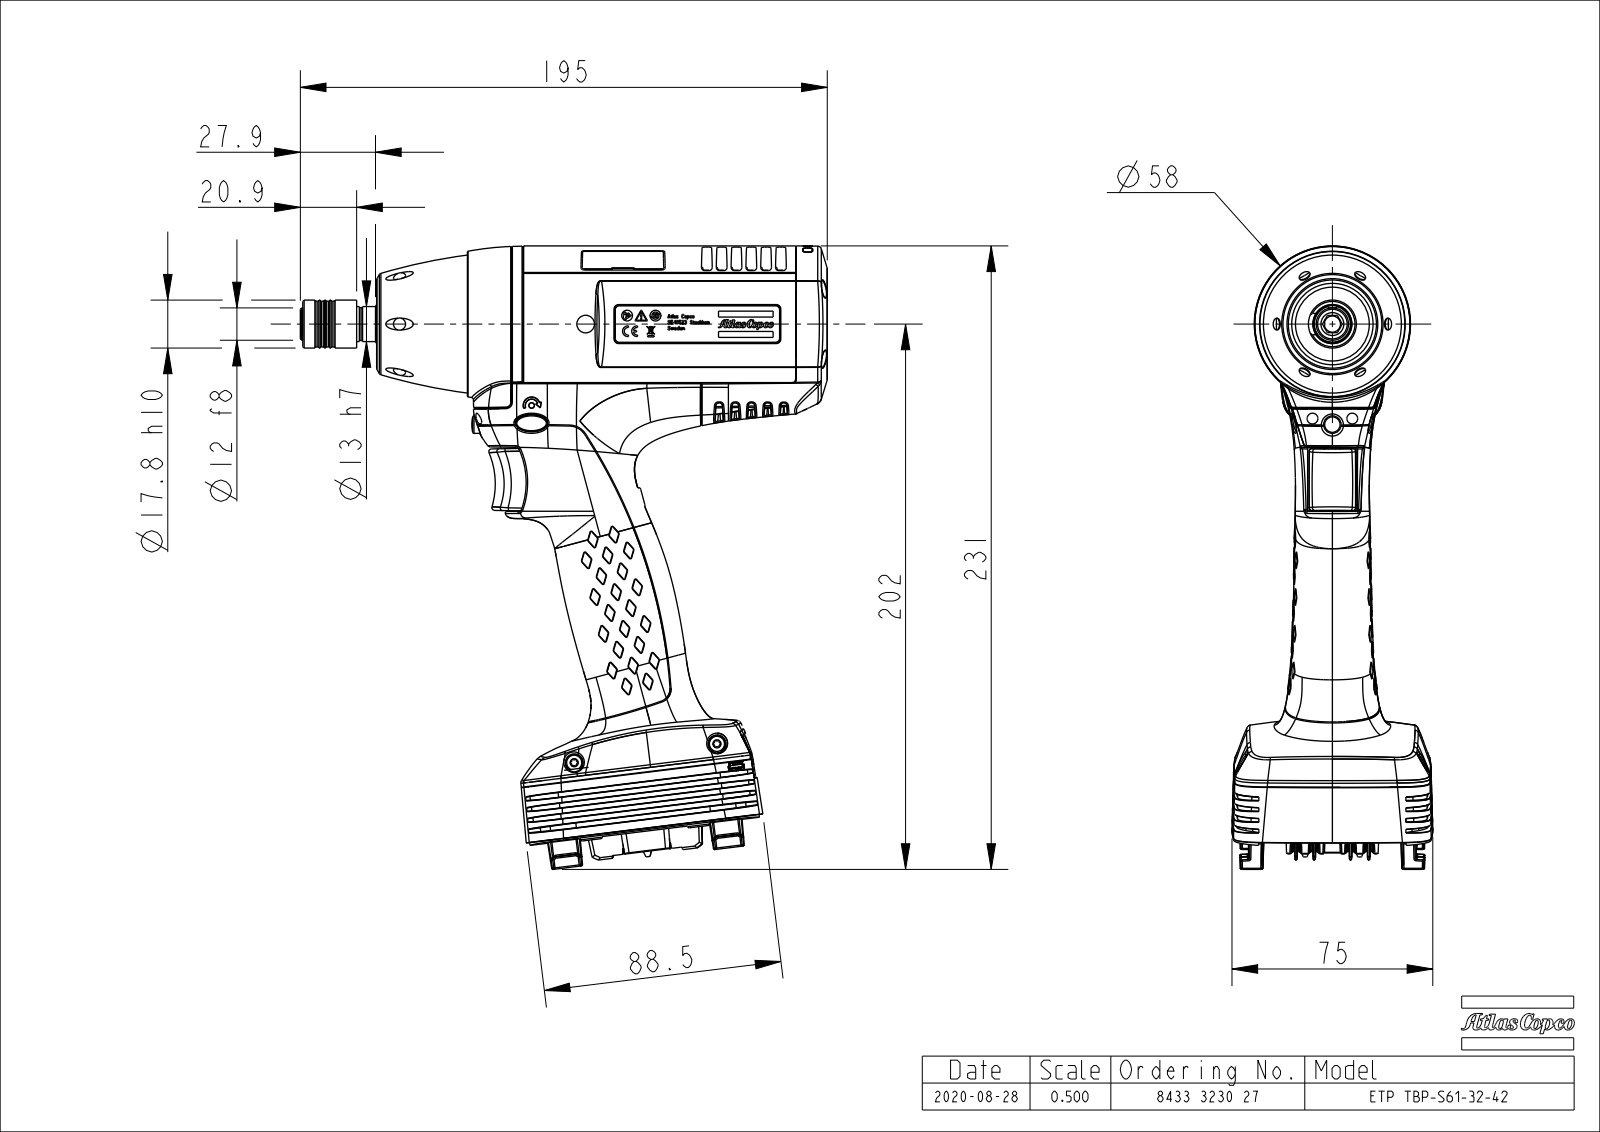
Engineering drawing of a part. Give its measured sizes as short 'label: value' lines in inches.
name: EXT_COMP_SW0001; PRT0009; PRT0015; 4250313204 (+1 more)
written by: CREO PARAMETRIC BY PTC INC, 2020281 (AP242_MANAGED_MODEL_BASED_3D_ENGINEERING_MIM_LF)
unit: in
bodies: 10 solids, 5885 faces (2462 planar, 1217 cylindrical, 2206 other)
size: 9.108 × 7.701 × 2.935
volume: 48.95 in³; area: 178.7 in²
holes: 3× ⌀0.126, 3× ⌀0.157, 3× ⌀0.177, 2× ⌀0.094, 2× ⌀0.138, 1× ⌀0.008, 1× ⌀0.016, 1× ⌀0.023, 1× ⌀0.04, 1× ⌀0.193, 1× ⌀0.22, 1× ⌀0.236
bosses: 7× ⌀0.22, 4× ⌀0.118, 1× ⌀1.457, 1× ⌀1.455, 1× ⌀0.701, 1× ⌀0.669, 1× ⌀0.512, 1× ⌀0.48
rounds: 152× R0.02, 98× R0.012, 78× R0.039, 62× R0.028, 60× R0.011, 60× R0.02, 42× R0.004, 26× R0.079
face distances: 0.878, 0.11, 0.075, 0.989, 4.367, 4.442, 0.217, 0.026, 0.059, 0.039
hole spacings: 0.891, 1.478, 0.213, 0.213, 0.262, 0.263, 0.27, 0.415
